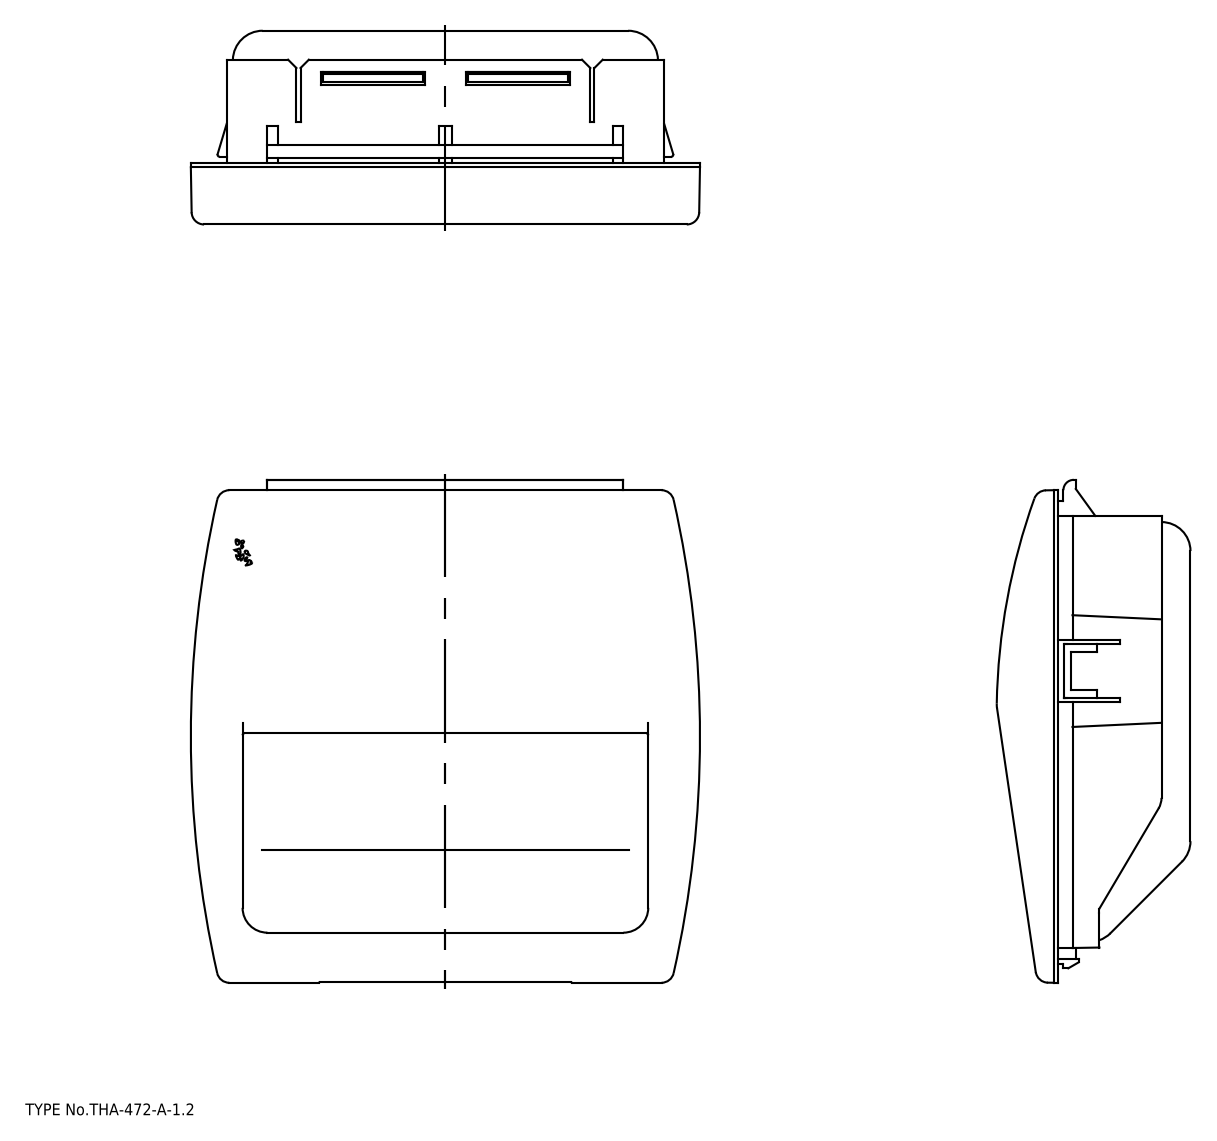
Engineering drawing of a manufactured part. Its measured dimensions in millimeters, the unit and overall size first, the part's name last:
Units: millimetres
Overall size (bounding box): 123 × 121.5 × 46.8
Round holes (diameter × count): ⌀3.4 ×2
Partial cylindrical surfaces — rounded edges, fillets, slot ends (radius × count): R0.5 ×114, R1 ×23, R7 ×21, R5 ×14, R0.3 ×11, R8.5 ×8, R0.6 ×4, R3 ×4
Main face-to-face distances: 2, 104.2, 1.5, 3.5, 100.7, 102.7, 102.2, 32, 30, 98.7
Hole centre spacings: 52
Volume: 107 561 mm³ · Surface area: 102 425 mm²
Bodies: 3 solids, 703 faces (273 planar, 266 cylindrical, 164 other)
Part name (STEP PRODUCT): 0020; j10488b0010 2020-03-24; J10488B0030
STEP written by: spGate 16.7.1 (AUTOMOTIVE_DESIGN)
